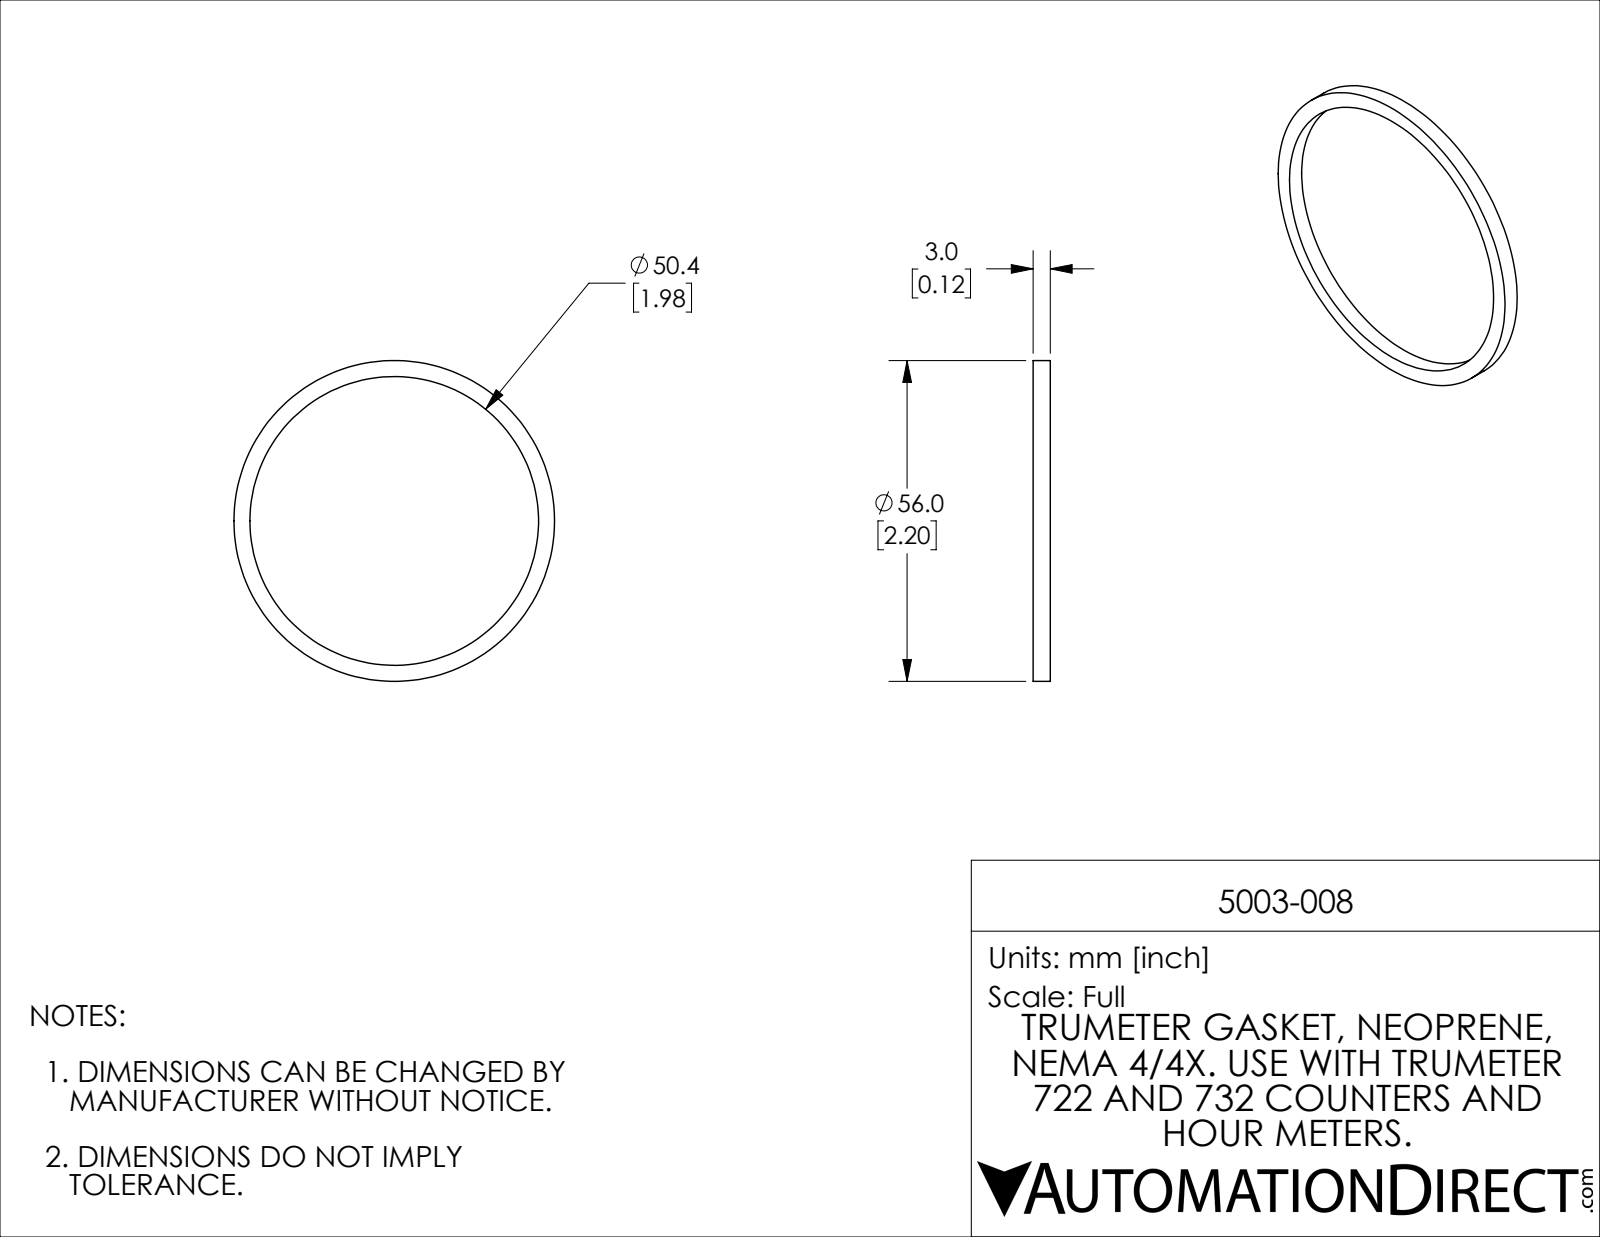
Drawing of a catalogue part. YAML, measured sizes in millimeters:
part_name: "5003-008"
step_written_by: "SolidWorks 2021 (CONFIG_CONTROL_DESIGN)"
units: millimeters
bodies: {solids: 1, faces: 6, planar: 2, cylindrical: 4, other: 0}
overall_size: [56, 56, 3]
volume: 1400
surface_area: 1939
round_holes:
  - {diameter: 50.4, count: 1}
round_bosses_or_shafts:
  - {diameter: 56, count: 1}
face_to_face_distances: [3]
